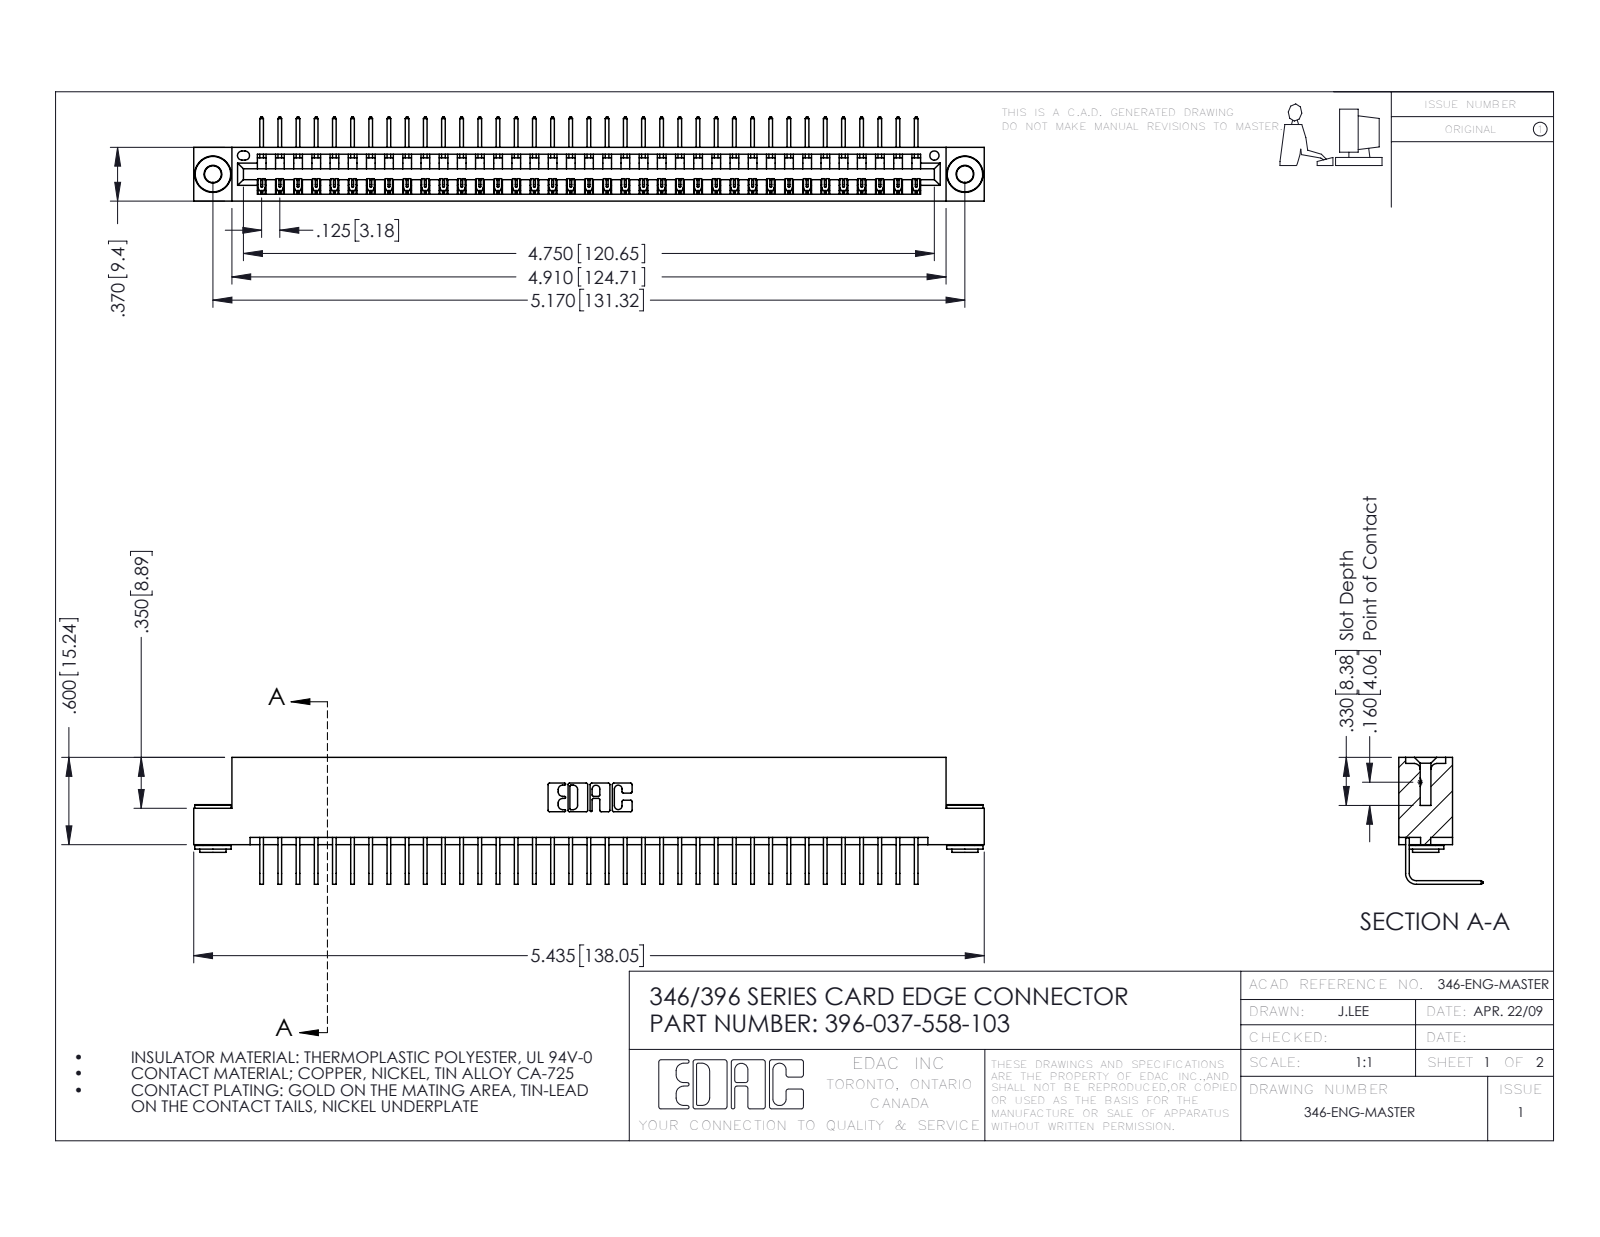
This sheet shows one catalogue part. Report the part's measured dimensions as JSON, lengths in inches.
{"part_name": "345-292-001_558 Tail - 2; 345-250-002_345-250-002-102; 346 Part_Flush Mounting Lugs - 0.156 Dia-TH; 396-037-558-103", "step_written_by": "SolidWorks 2016 (CONFIG_CONTROL_DESIGN)", "units": "inches", "bodies": {"solids": 40, "faces": 2380, "planar": 1640, "cylindrical": 732, "other": 8}, "overall_size": [5.435, 0.873, 0.58], "volume_in3": 0.813, "surface_area_in2": 27.21, "round_holes": [[0.116, 2], [0.156, 2], [0.064, 1]], "round_bosses_or_shafts": [[0.25, 2], [0.18, 2], [0.136, 2]], "partial_cylinders_radius": [[0.006, 74], [0.01, 22], [0.007, 6], [0.031, 6], [0.026, 3], [0.031, 2], [0.04, 2], [0.014, 1]], "face_to_face_distances": [0.322, 0.048, 0.37, 0.25, 0.025, 0.298, 0.072, 0.148, 0.222, 0.1], "hole_center_spacings": [0.246, 4.961, 5.17]}
